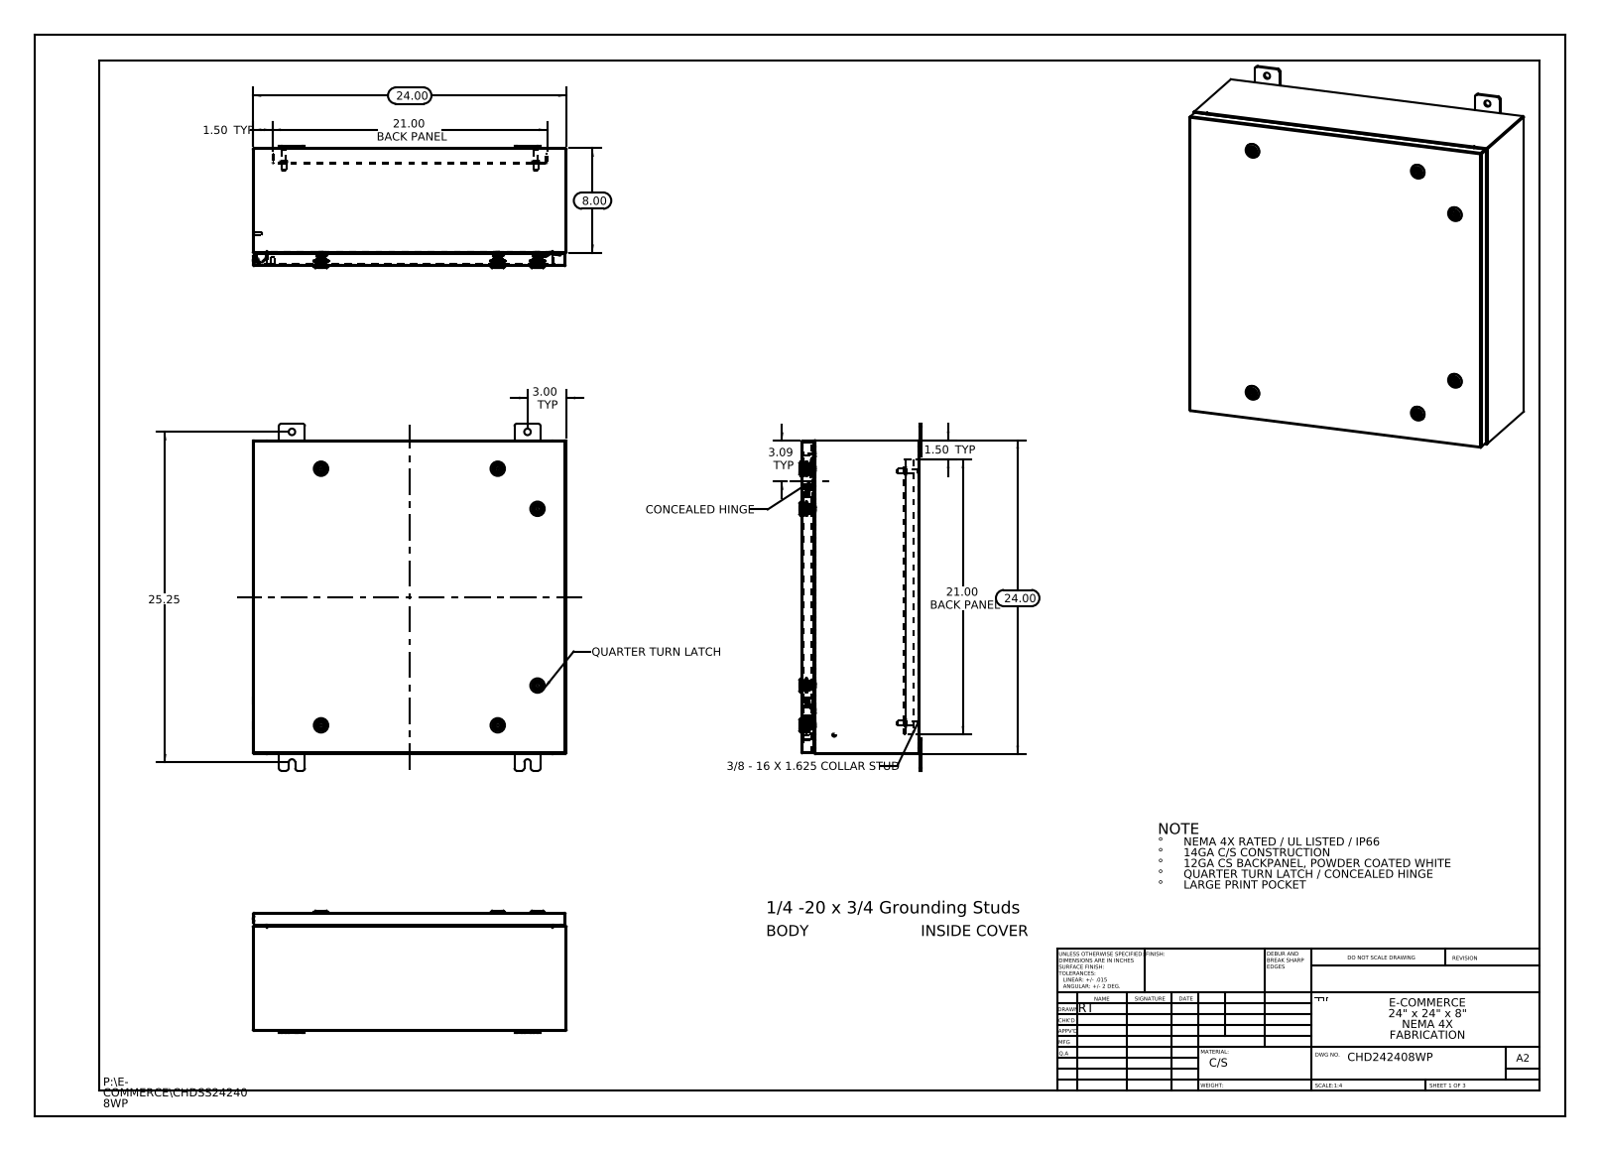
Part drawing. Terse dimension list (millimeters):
name: CHDSS242408WP Mounting Feet; Concealed Hinge (Cover Side); CHDSS242408WP Top; Concealed Hinge enclosure side (+8 more)
written by: SolidWorks 2013 (CONFIG_CONTROL_DESIGN)
unit: mm
bodies: 55 solids, 5420 faces (1592 planar, 1692 cylindrical, 2136 other)
size: 673.1 × 609.6 × 237.6
volume: 3 582 000 mm³; area: 3 518 000 mm²
holes: 8× ⌀12.7, 6× ⌀5, 6× ⌀10, 6× ⌀10.2, 6× ⌀16, 6× ⌀20, 4× ⌀3.5, 2× ⌀5.4
bosses: 8× ⌀6, 6× ⌀28, 6× ⌀19.8, 6× ⌀15.9, 6× ⌀15.5, 6× ⌀13.5, 6× ⌀10, 6× ⌀2.9
rounds: 198× R0.2, 198× R3, 72× R0.7, 24× R0.5, 24× R4.8, 24× R5, 20× R0.3, 18× R2.2
face distances: 1.9, 607.7, 1.9, 228.9, 226.9, 227, 225.1, 2.6, 25.4, 27.3
hole spacings: 342.9, 47.2, 73.1, 77.9, 416, 427.1, 457.2, 489
